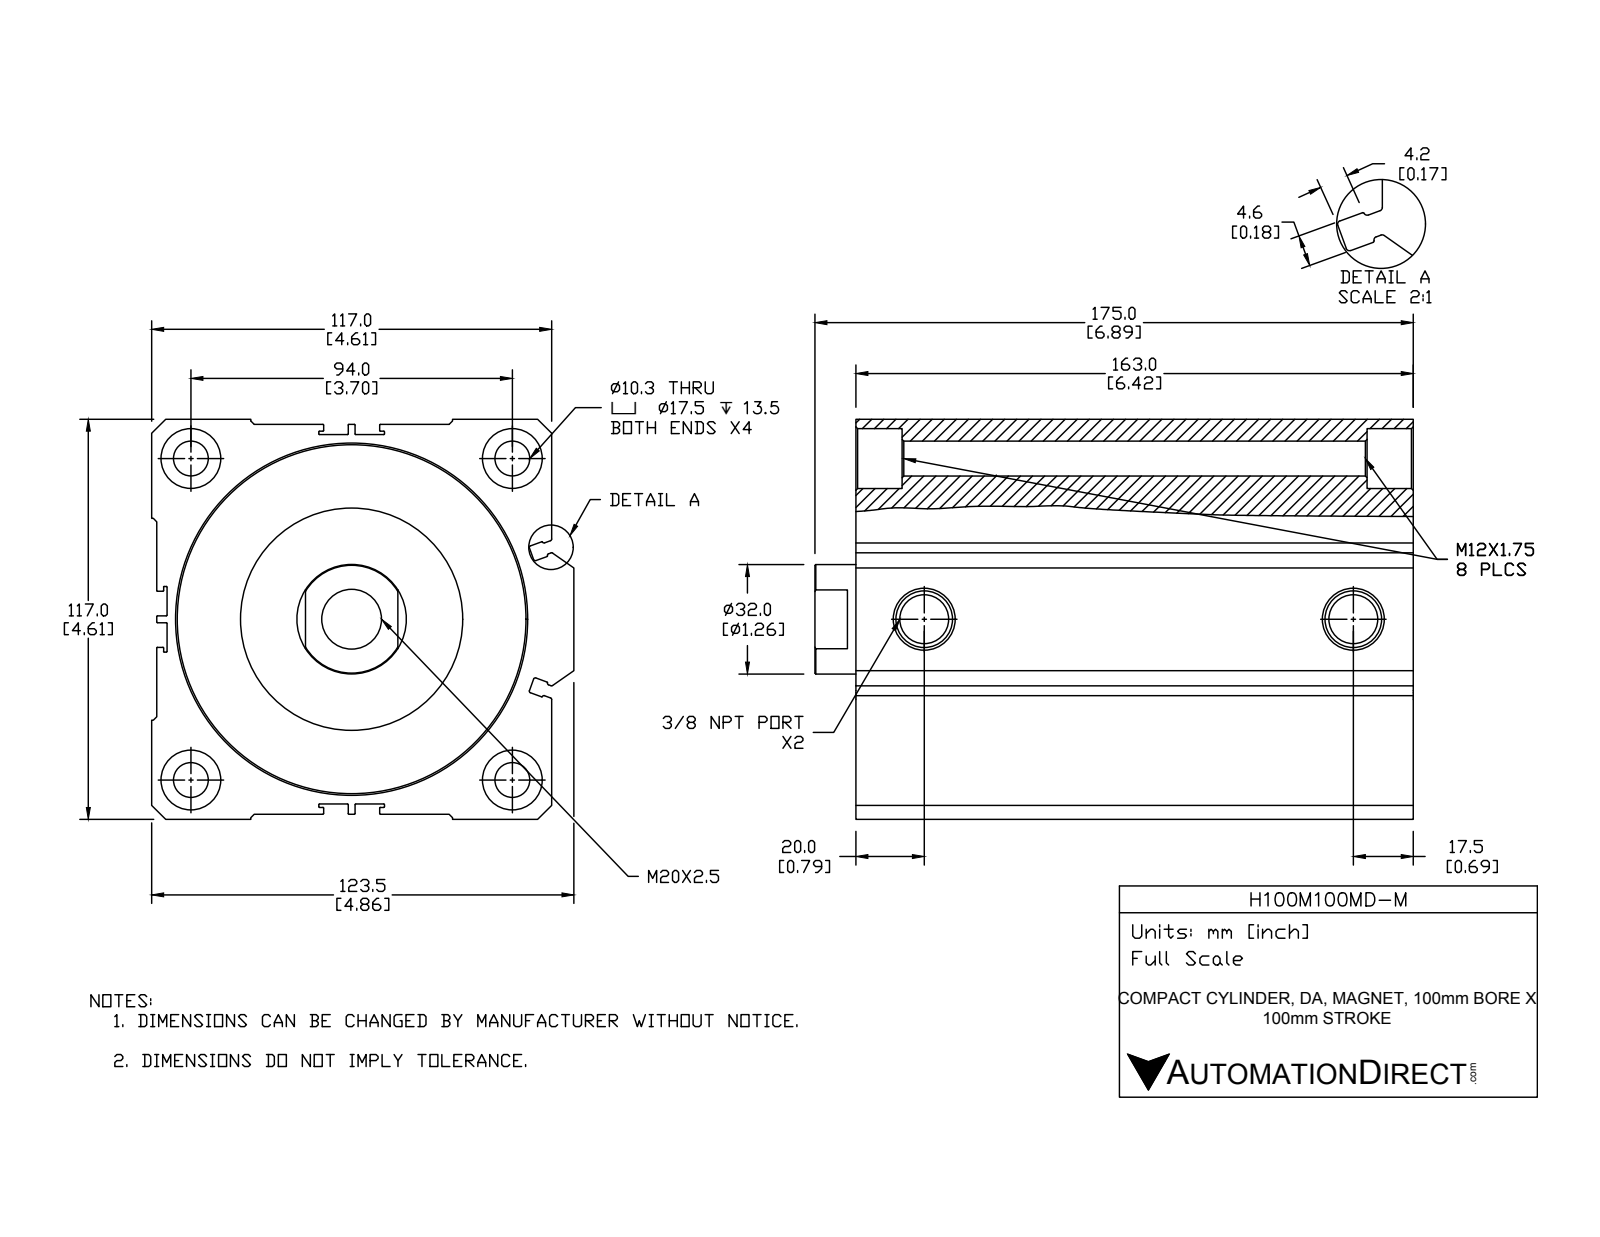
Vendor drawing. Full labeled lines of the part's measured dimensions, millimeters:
Part name (STEP PRODUCT): H100M100MD-M; H100M100MD-M-PISTON; H100M100MD-M-BODY
STEP written by: SolidWorks 2015 (CONFIG_CONTROL_DESIGN)
Units: millimetres
Bodies: 2 solids, 261 faces (105 planar, 103 cylindrical, 53 other)
Overall size (bounding box): 175 × 123.5 × 117
Volume: 1 341 000 mm³ · Surface area: 241 374 mm²
Round holes (diameter × count): ⌀17.5 ×5, ⌀10.2 ×4, ⌀14.27 ×2, ⌀32 ×1, ⌀65 ×1, ⌀100 ×1, ⌀102 ×1
Round bosses / shafts (diameter × count): ⌀39 ×1
Partial cylindrical surfaces — rounded edges, fillets, slot ends (radius × count): R0.2 ×40, R0.5 ×12
Main face-to-face distances: 1.5, 115.5, 117, 112.5, 4.5, 3, 27.8, 128.5, 100.7, 114
Hole centre spacings: 66.47, 94, 132.94, 125.5
